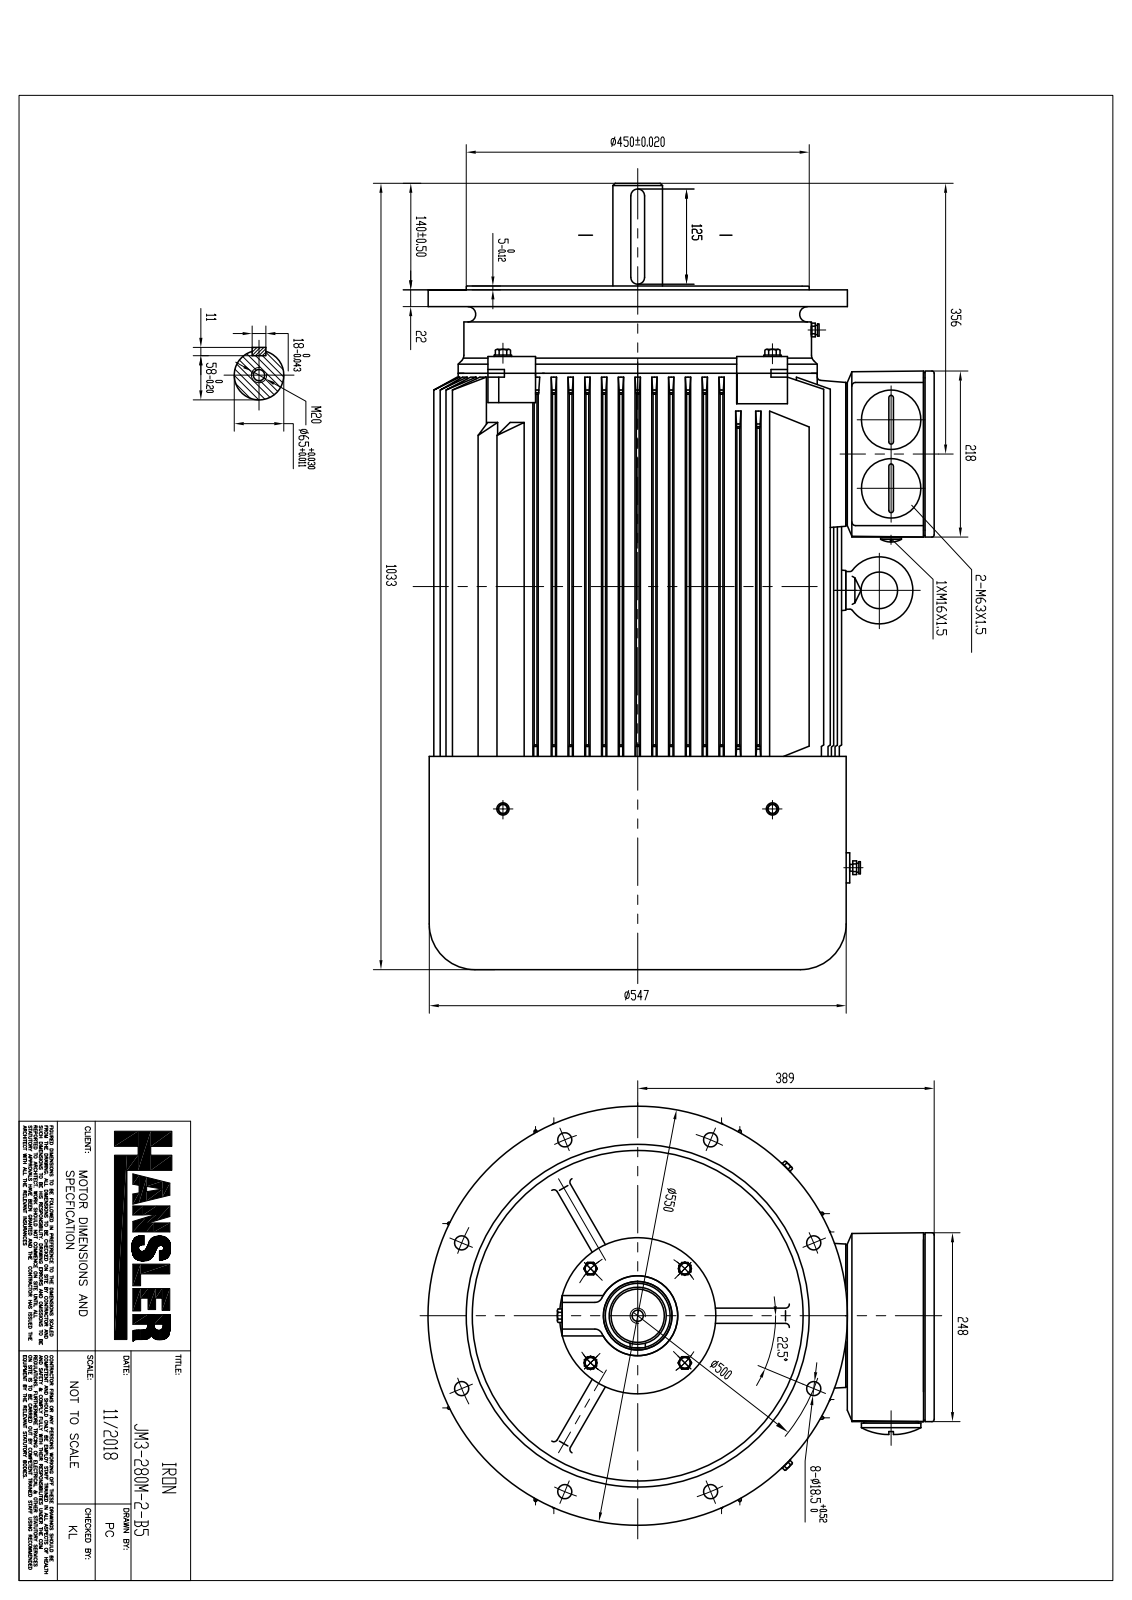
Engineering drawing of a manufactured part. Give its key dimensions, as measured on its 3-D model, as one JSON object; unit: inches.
{"part_name": "pc0534AA92lzx9", "step_written_by": "SIEMENS PLM Software NX 8.5 (AUTOMOTIVE_DESIGN)", "units": "inches", "bodies": {"solids": 59, "faces": 7094, "planar": 4617, "cylindrical": 1159, "other": 1318}, "overall_size": [38.642, 29.409, 26.092], "volume_in3": 2296, "surface_area_in2": 11850, "round_holes": [[0.472, 16], [0.315, 12], [0.394, 10], [0.571, 8], [0.748, 8], [0.33, 4], [0.331, 4], [0.441, 4], [0.494, 4], [0.496, 4], [1.705, 2], [2.015, 2]], "round_bosses_or_shafts": [[0.738, 4], [0.63, 4], [0.496, 4], [0.428, 4], [0.394, 4], [0.356, 4], [0.315, 4], [0.283, 4]], "partial_cylinders_radius": [[0.197, 182], [0.157, 152], [0.236, 70], [0.079, 24], [0.315, 16], [0.394, 10], [0.039, 9], [0.118, 6]], "face_to_face_distances": [0.918, 12.246, 11.572, 9.678, 12.246, 2.776, 7.666, 0.866, 1.909, 13.164], "hole_center_spacings": [3.445, 5.391, 5.984, 6.403, 6.89, 13.919, 4.872, 7.533]}
